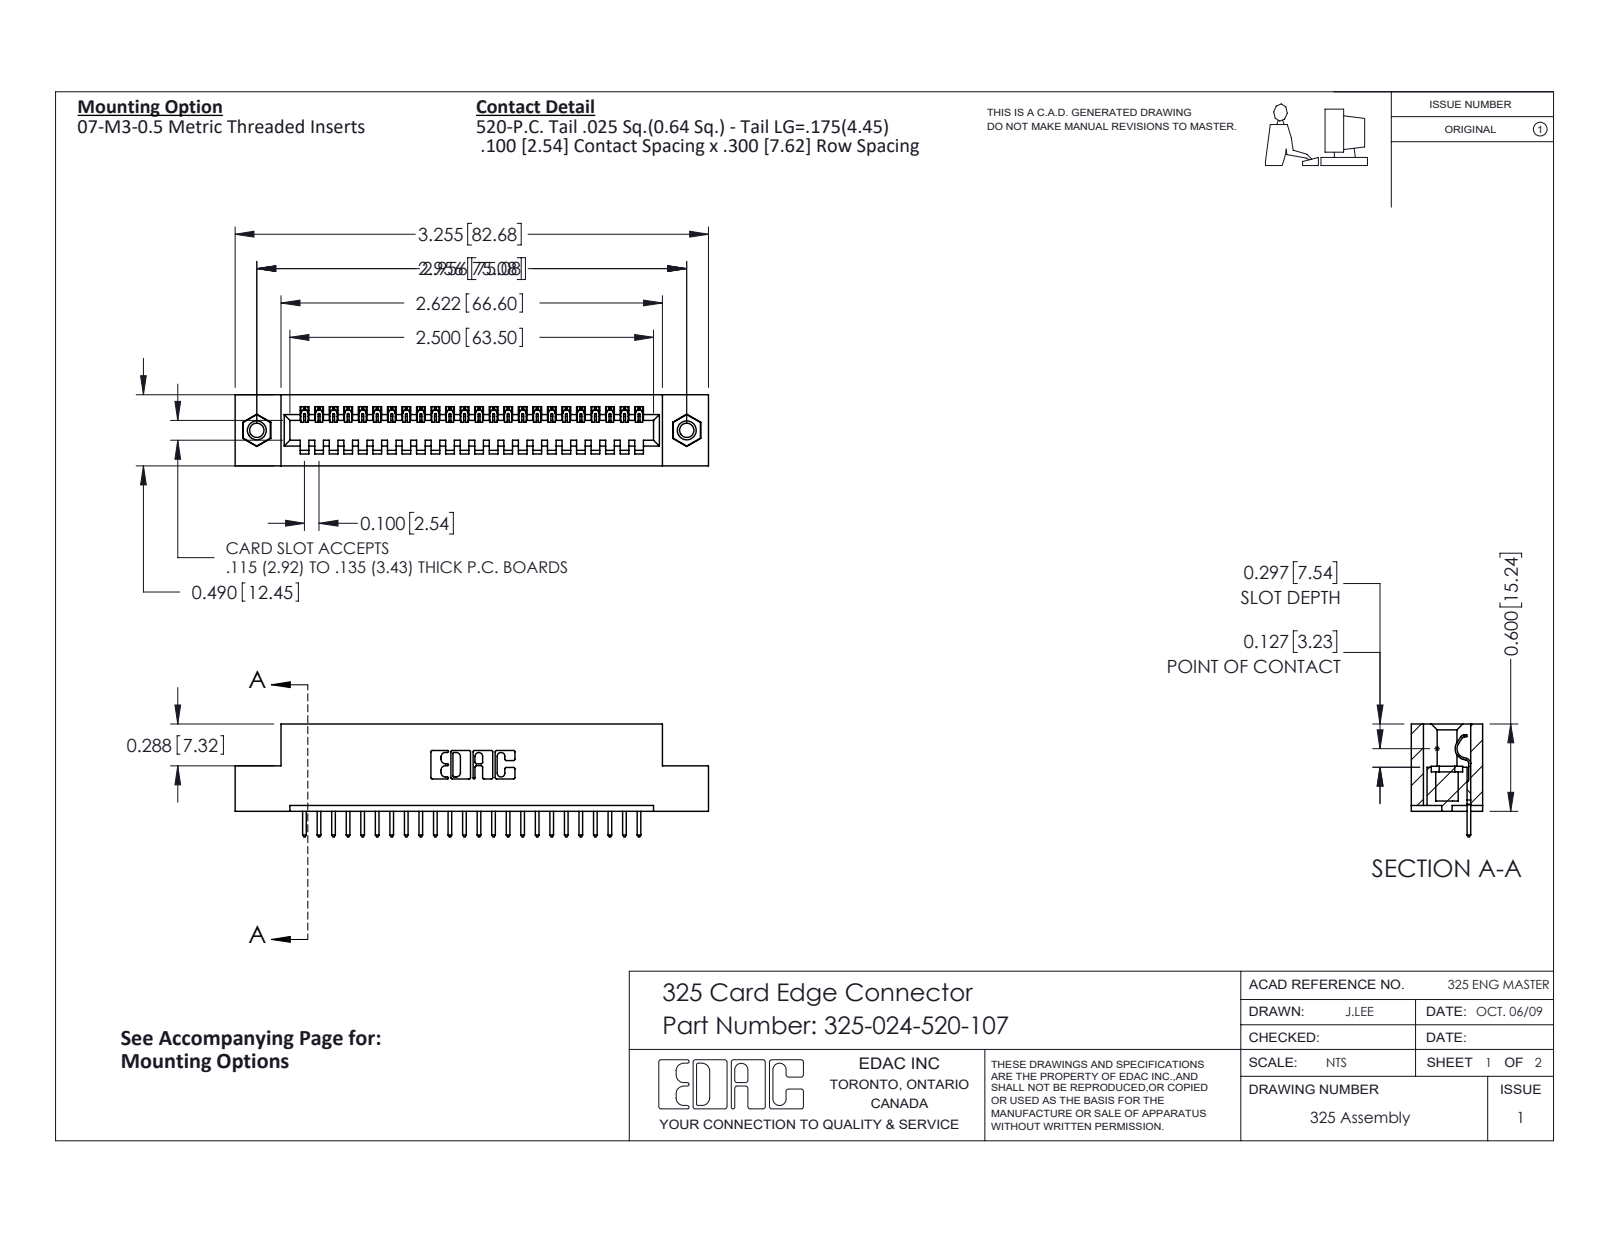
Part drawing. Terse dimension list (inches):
name: 325-024-520-107; 325-292-001_325-293-120; 325 Part_TI; 345-250-001_345-250-005-103
written by: SolidWorks 2016 (CONFIG_CONTROL_DESIGN)
unit: in
bodies: 27 solids, 1566 faces (1110 planar, 440 cylindrical, 16 other)
size: 3.255 × 0.775 × 0.49
volume: 0.627 in³; area: 16.58 in²
holes: 2× ⌀0.098, 2× ⌀0.125, 2× ⌀0.16
bosses: 2× ⌀0.155
rounds: 48× R0.006, 48× R0.01, 22× R0.01, 6× R0.007, 6× R0.031, 3× R0.026, 1× R0.014, 1× R0.022
face distances: 0.083, 0.407, 0.49, 0.3, 0.107, 0.383, 0.025, 0.04, 0.325, 0.6
hole spacings: 2.956
